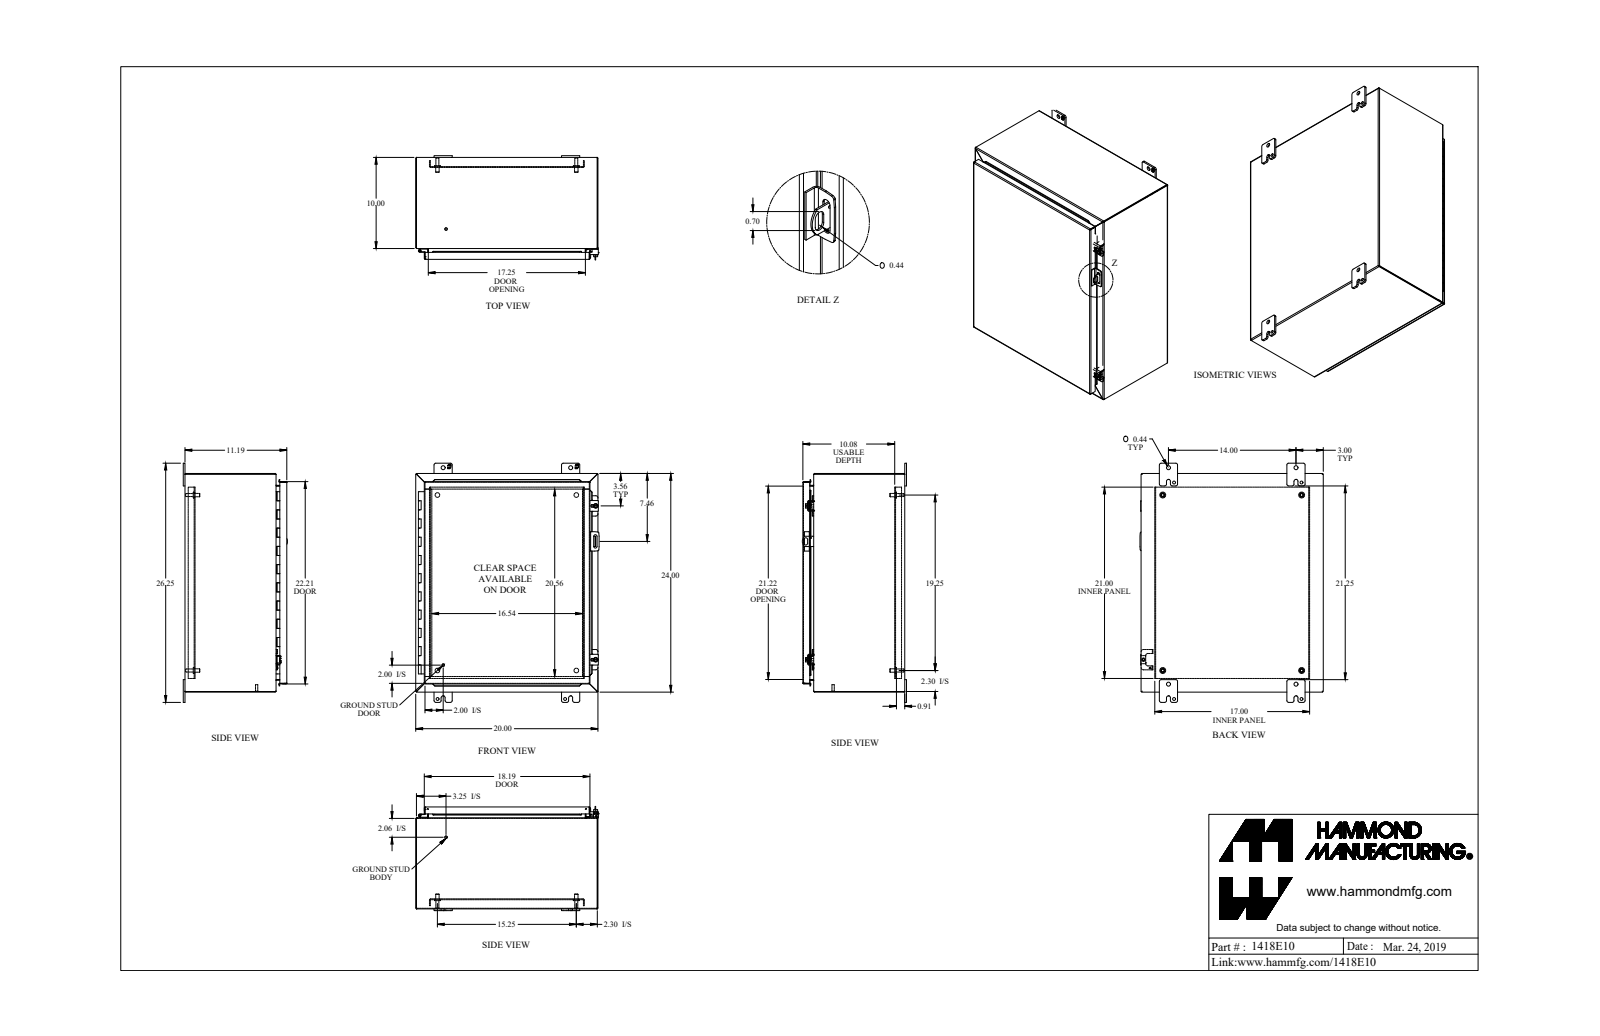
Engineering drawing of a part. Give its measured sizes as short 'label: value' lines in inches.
name: 1418E10
written by: SolidWorks 2019 (AUTOMOTIVE_DESIGN)
unit: in
bodies: 38 solids, 1010 faces (693 planar, 263 cylindrical, 54 other)
size: 26.25 × 20.125 × 11.437
volume: 202 in³; area: 5 261 in²
holes: 4× ⌀0.313, 4× ⌀0.437, 4× ⌀0.5, 2× ⌀0.213, 2× ⌀0.265, 2× ⌀0.307, 2× ⌀0.375, 2× ⌀0.445, 1× ⌀0.125, 1× ⌀0.187
bosses: 4× ⌀0.65, 4× ⌀0.375, 4× ⌀0.33, 2× ⌀1, 2× ⌀0.5, 2× ⌀0.39, 2× ⌀0.281, 2× ⌀0.25
rounds: 26× R0.188, 20× R0.036, 20× R0.108, 13× R0.048, 13× R0.143, 8× R0.007, 8× R0.045, 8× R0.079
face distances: 0.072, 11.113, 11.041, 19.928, 11.185, 0.937, 23.928, 0.095, 1.009, 10.081
hole spacings: 14, 1.735, 22.259, 23.75, 27.569, 3.065, 3.125, 14.7
